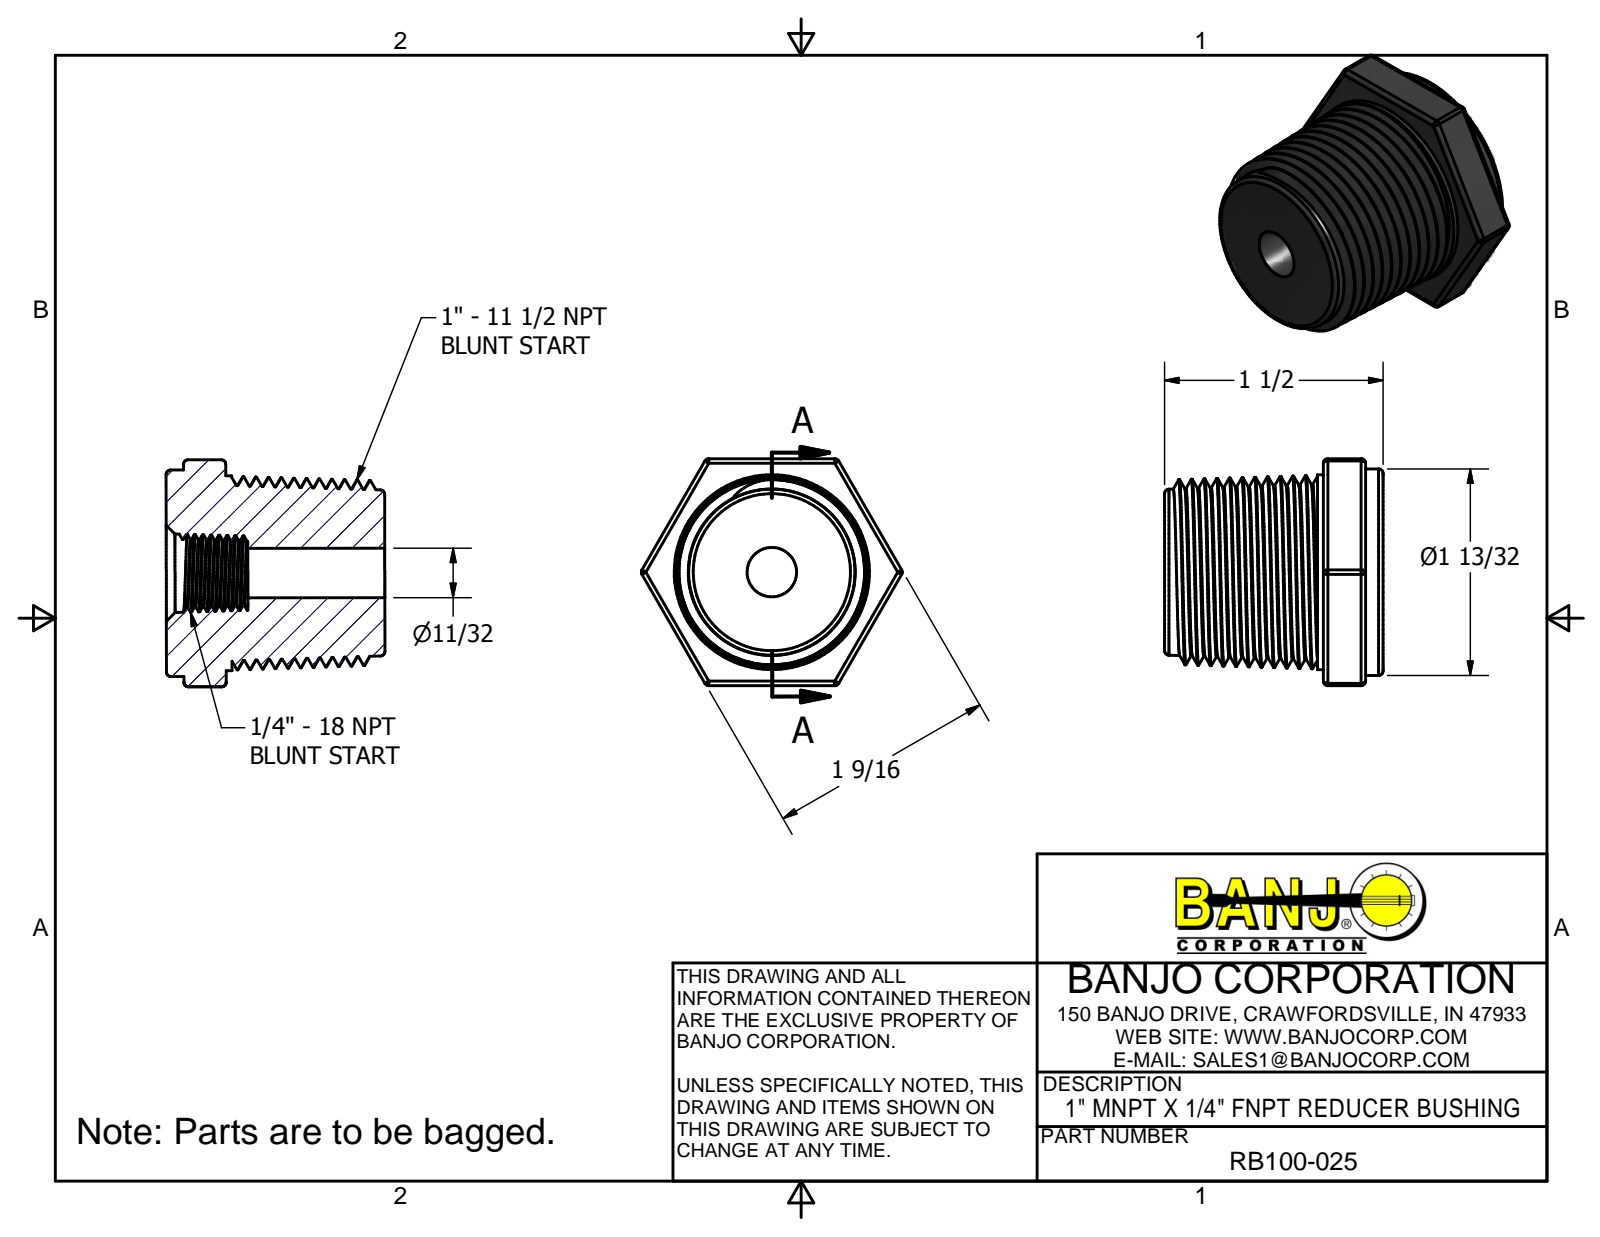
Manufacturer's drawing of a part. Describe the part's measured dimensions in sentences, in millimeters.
The part is named "RB100-025". Its 3-D file was written by "Autodesk Inventor 2014 (AUTOMOTIVE_DESIGN)". It is 1 solid with 82 faces: 12 planar, 24 cylindrical and 46 other. Overall it measures 45.51 by 39.62 by 38.1 millimeters. Its volume is 31 163 cubic millimeters and its surface area 9 841 square millimeters. Round holes: 1 of diameter 8.64. Round bosses or shafts: 1 of diameter 36.07, 1 of diameter 34.04. Partial cylindrical surfaces (rounded edges, fillets, slot ends): 18 of radius 0.79, 1 of radius 4.36, 1 of radius 8.89. The main face-to-face distances are 38.1, 39.62, 10.41, 27.69, 3.05, 7.36, 35.05, 11.43, 8.38, 1.02.
